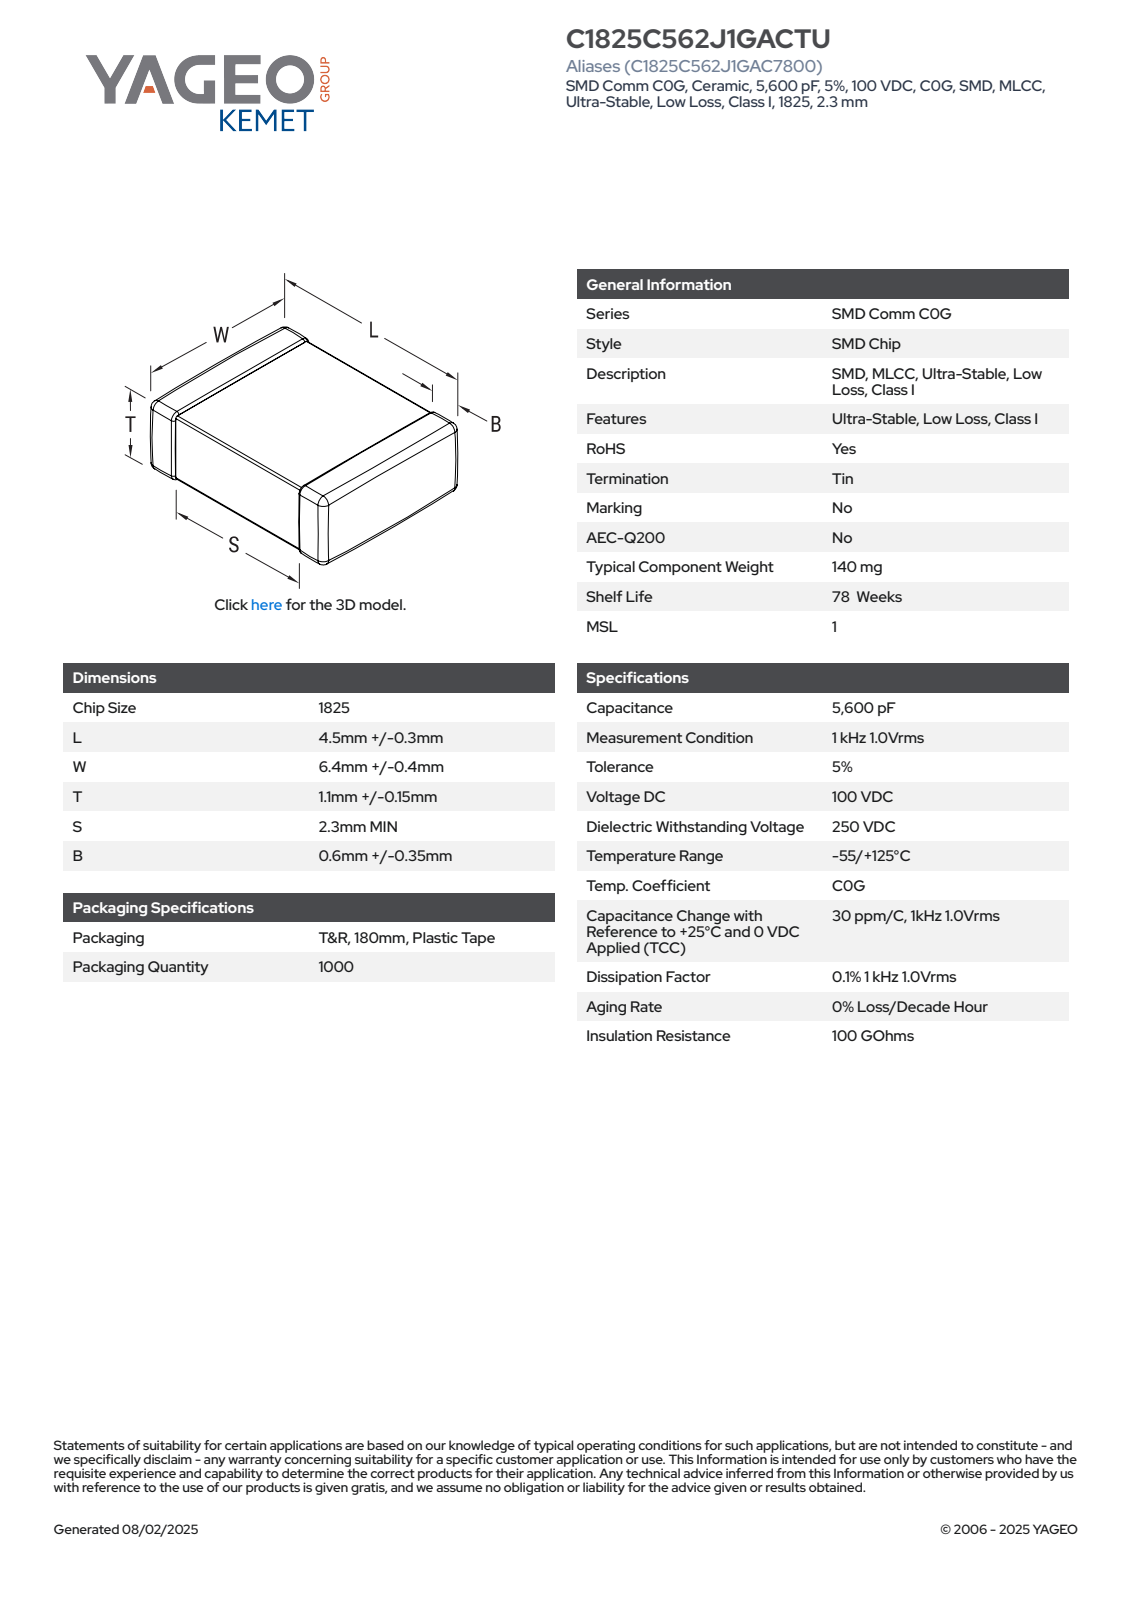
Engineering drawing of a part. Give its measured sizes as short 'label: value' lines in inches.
name: CCS_CCSTD_1825_L4.8W6.8T1.25B0.6
written by: SolidWorks 2021 (AUTOMOTIVE_DESIGN)
unit: in
bodies: 4 solids, 129 faces (71 planar, 42 cylindrical, 16 other)
size: 0.268 × 0.189 × 0.049
volume: 0.002 in³; area: 0.15 in²
rounds: 24× R0.006
face distances: 0.038, 0.044, 0.049, 0.189, 0.262, 0.257, 0.268, 0.063, 0.126, 0.102
